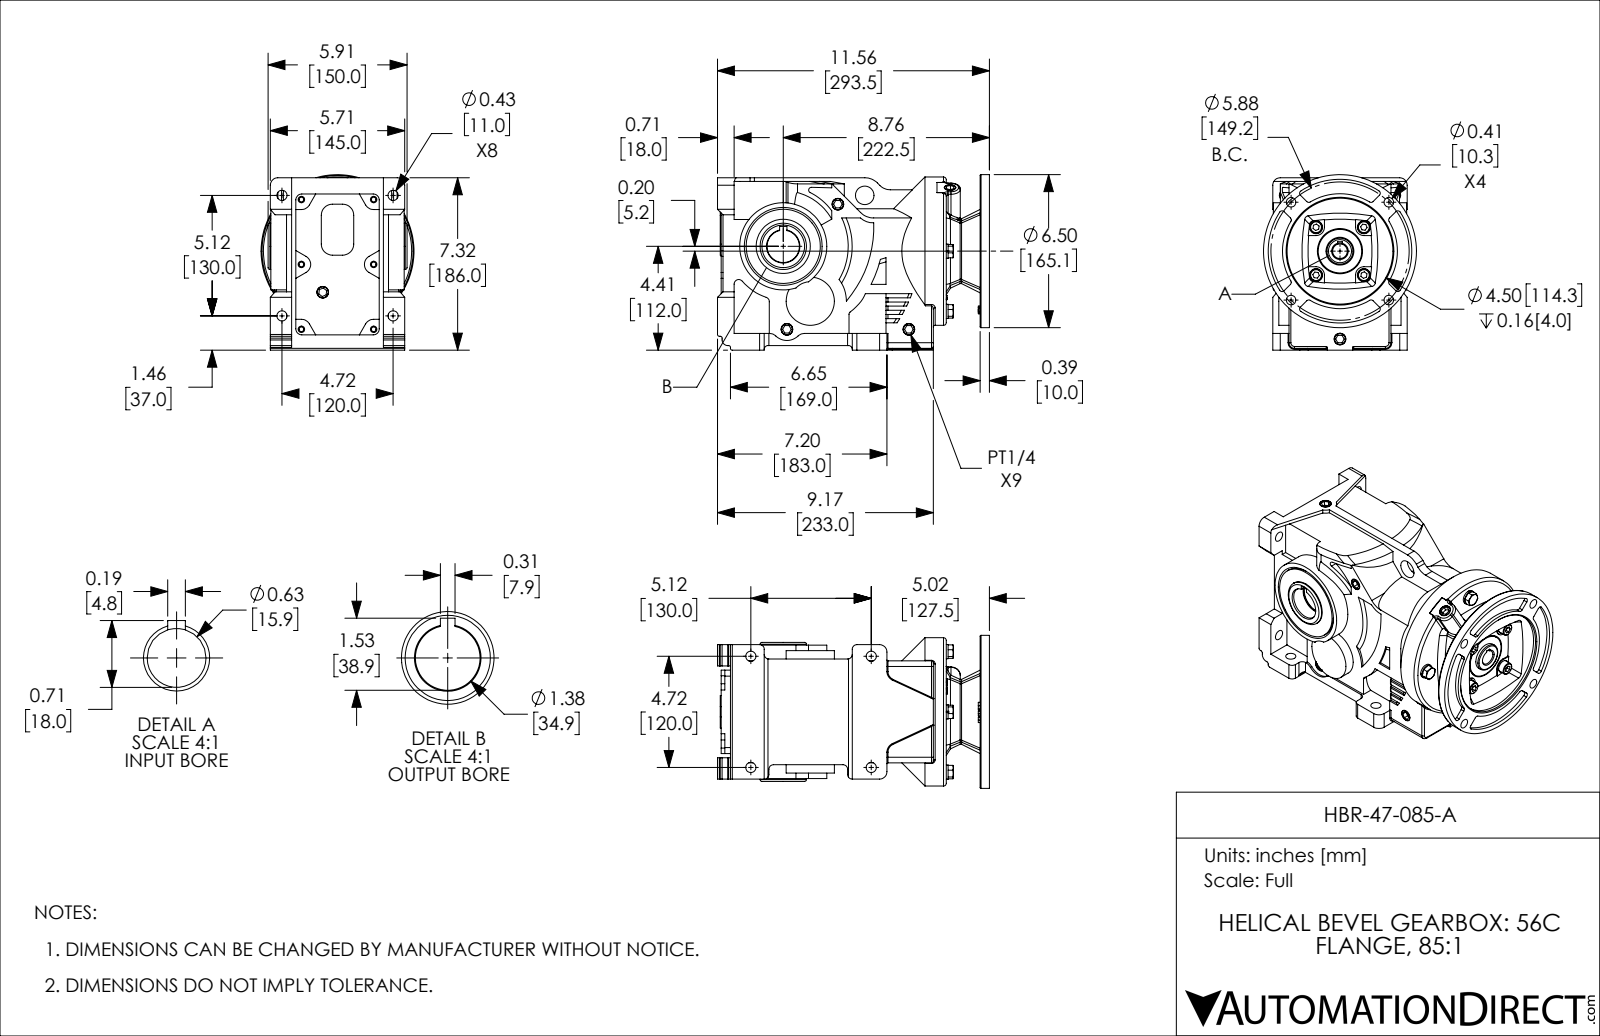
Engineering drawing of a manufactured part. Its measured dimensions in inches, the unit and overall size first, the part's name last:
Units: inches
Overall size (bounding box): 11.555 × 7.455 × 6.5
Round holes (diameter × count): ⌀0.433 ×8, ⌀0.197 ×6, ⌀0.276 ×6, ⌀0.323 ×4, ⌀0.354 ×4, ⌀0.406 ×4, ⌀0.551 ×4, ⌀0.625 ×1, ⌀0.787 ×1, ⌀0.846 ×1, ⌀1.375 ×1, ⌀1.457 ×1
Round bosses / shafts (diameter × count): ⌀0.606 ×4, ⌀0.512 ×4, ⌀0.315 ×4, ⌀6.5 ×1, ⌀6.299 ×1, ⌀3.701 ×1, ⌀3.15 ×1, ⌀2.047 ×1
Partial cylindrical surfaces — rounded edges, fillets, slot ends (radius × count): R0.118 ×22, R0.079 ×18, R0.394 ×12, R0.197 ×10, R0.472 ×9, R0.039 ×5, R0.256 ×4, R0.315 ×4
Main face-to-face distances: 0.197, 0.394, 0.236, 0.157, 11.004, 4.331, 0.118, 0.079, 11.24, 10.846
Hole centre spacings: 1.848, 2.132, 3.27, 3.717, 5.08, 5.118, 1.437, 1.5
Volume: 308.7 in³ · Surface area: 495.3 in²
Bodies: 1 solid, 1002 faces (447 planar, 317 cylindrical, 238 other)
Part name (STEP PRODUCT): HBR-47-085-A
STEP written by: SolidWorks 2018 (AUTOMOTIVE_DESIGN)
